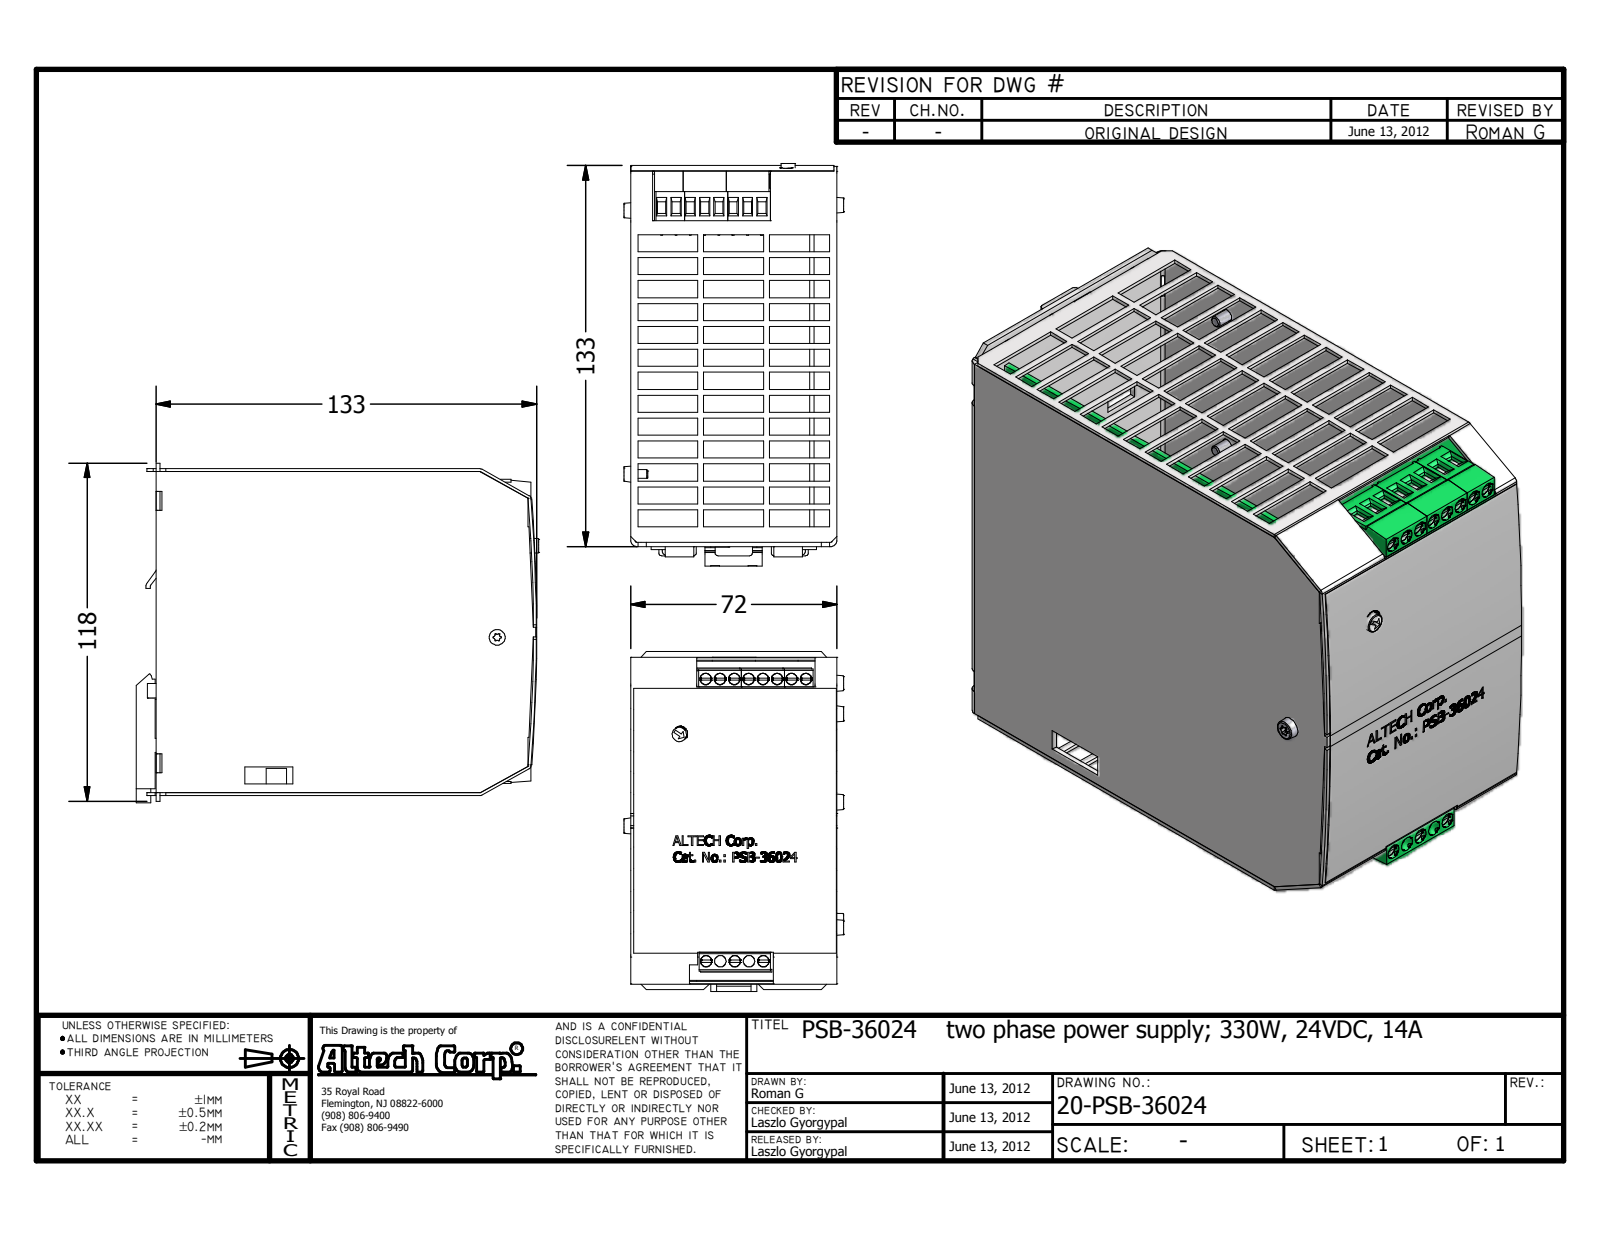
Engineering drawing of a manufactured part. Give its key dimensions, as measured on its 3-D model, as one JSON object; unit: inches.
{"part_name": "ALTECH-PSB-36024", "step_written_by": "Autodesk Inventor 2013 (CONFIG_CONTROL_DESIGN)", "units": "inches", "bodies": {"solids": 1, "faces": 2439, "planar": 1783, "cylindrical": 412, "other": 244}, "overall_size": [5.534, 4.671, 3.024], "volume_in3": 7.02, "surface_area_in2": 247.6, "round_holes": [[0.039, 53], [0.157, 13], [0.13, 6], [0.035, 4], [0.079, 2]], "round_bosses_or_shafts": [[0.152, 11], [0.055, 11], [0.118, 6], [0.105, 6], [0.06, 2], [0.354, 1], [0.197, 1], [0.11, 1]], "partial_cylinders_radius": [[0.004, 52], [0.01, 37], [0.022, 36], [0.008, 17], [0.02, 11], [0.039, 8], [0.059, 8], [0.02, 4]], "face_to_face_distances": [0.059, 2.776, 0.063, 2.835, 2.717, 0.315, 0.311, 0.252, 2.465, 2.524], "hole_center_spacings": [0.1, 0.197, 0.394, 3.778, 0.591, 0.787, 3.878, 3.883]}
